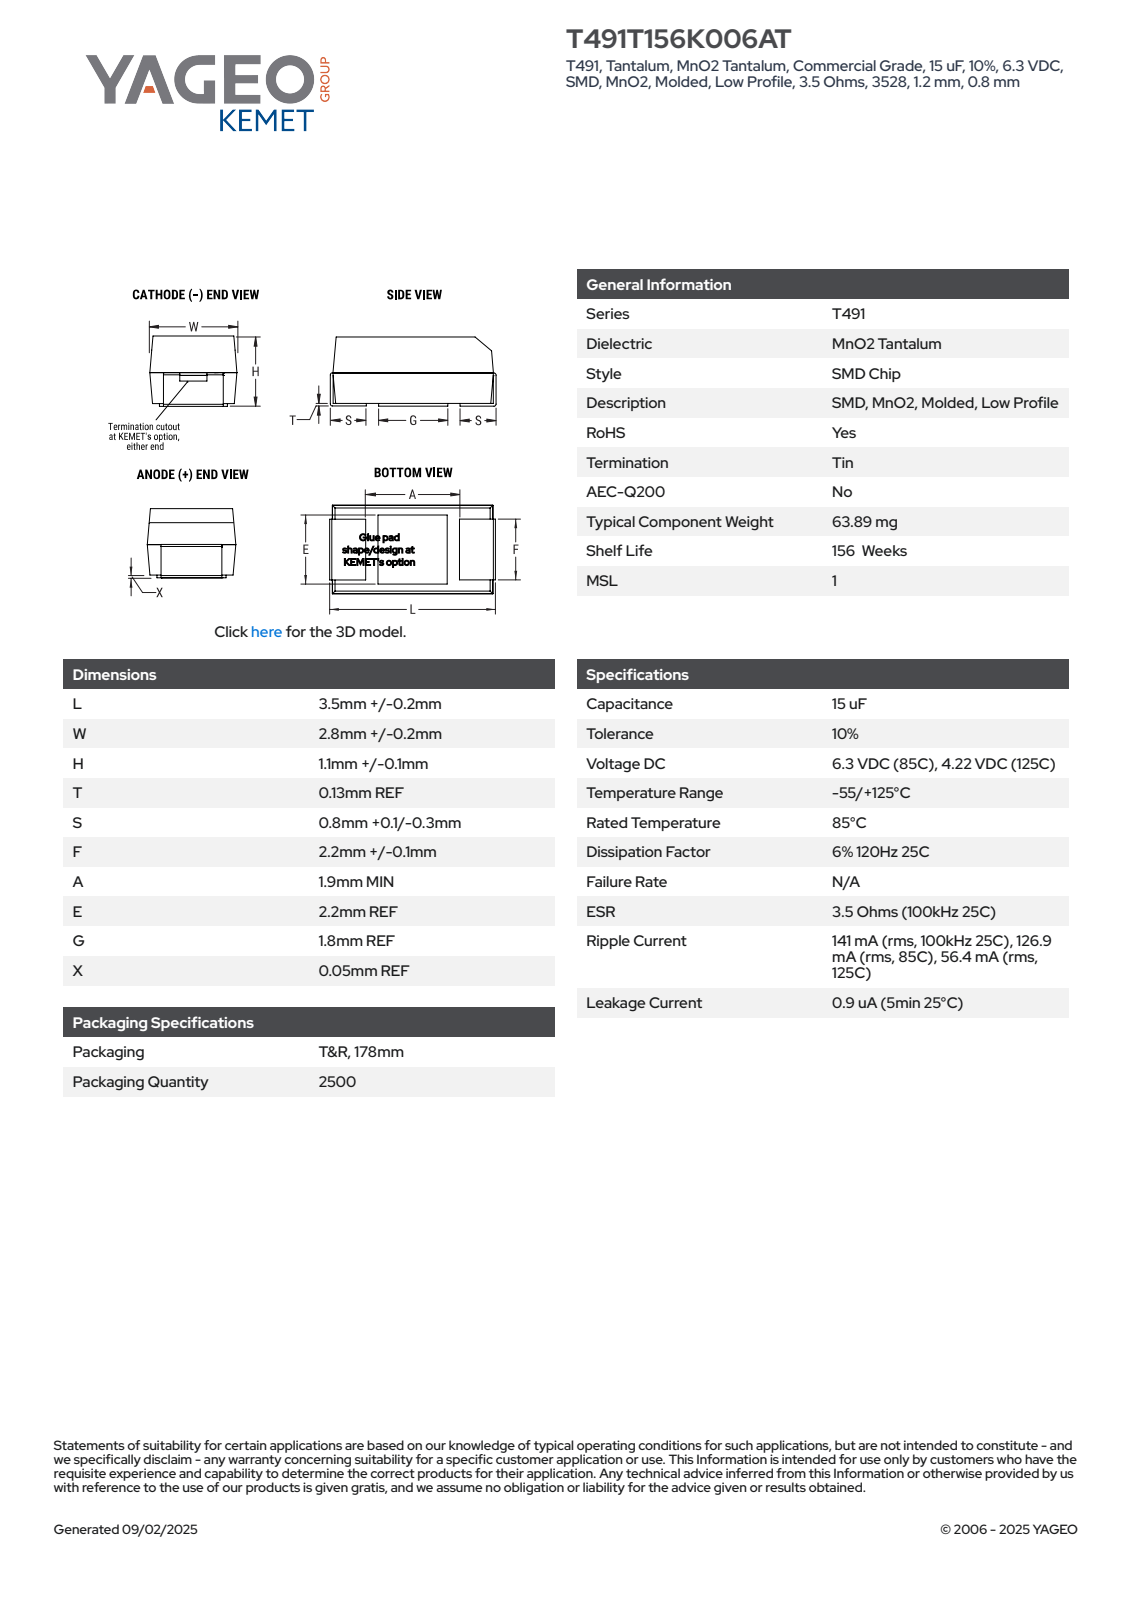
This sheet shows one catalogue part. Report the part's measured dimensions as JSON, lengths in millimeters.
{"part_name": "CTSM_TCM2NBKRP_3528_L3.7W3H1.2T0.13S0.8F2.3A1.9E2.2G1.8X0.05", "step_written_by": "SolidWorks 2020 (AUTOMOTIVE_DESIGN)", "units": "millimeters", "bodies": {"solids": 4, "faces": 94, "planar": 90, "cylindrical": 4, "other": 0}, "overall_size": [3.7, 3, 1.21], "volume_mm3": 11, "surface_area_mm2": 38, "partial_cylinders_radius": [[0.1, 4]], "face_to_face_distances": [1.2, 2.89, 2.88, 3.57, 1.15, 3.7, 3.44, 1.07, 0.6, 0.95]}
